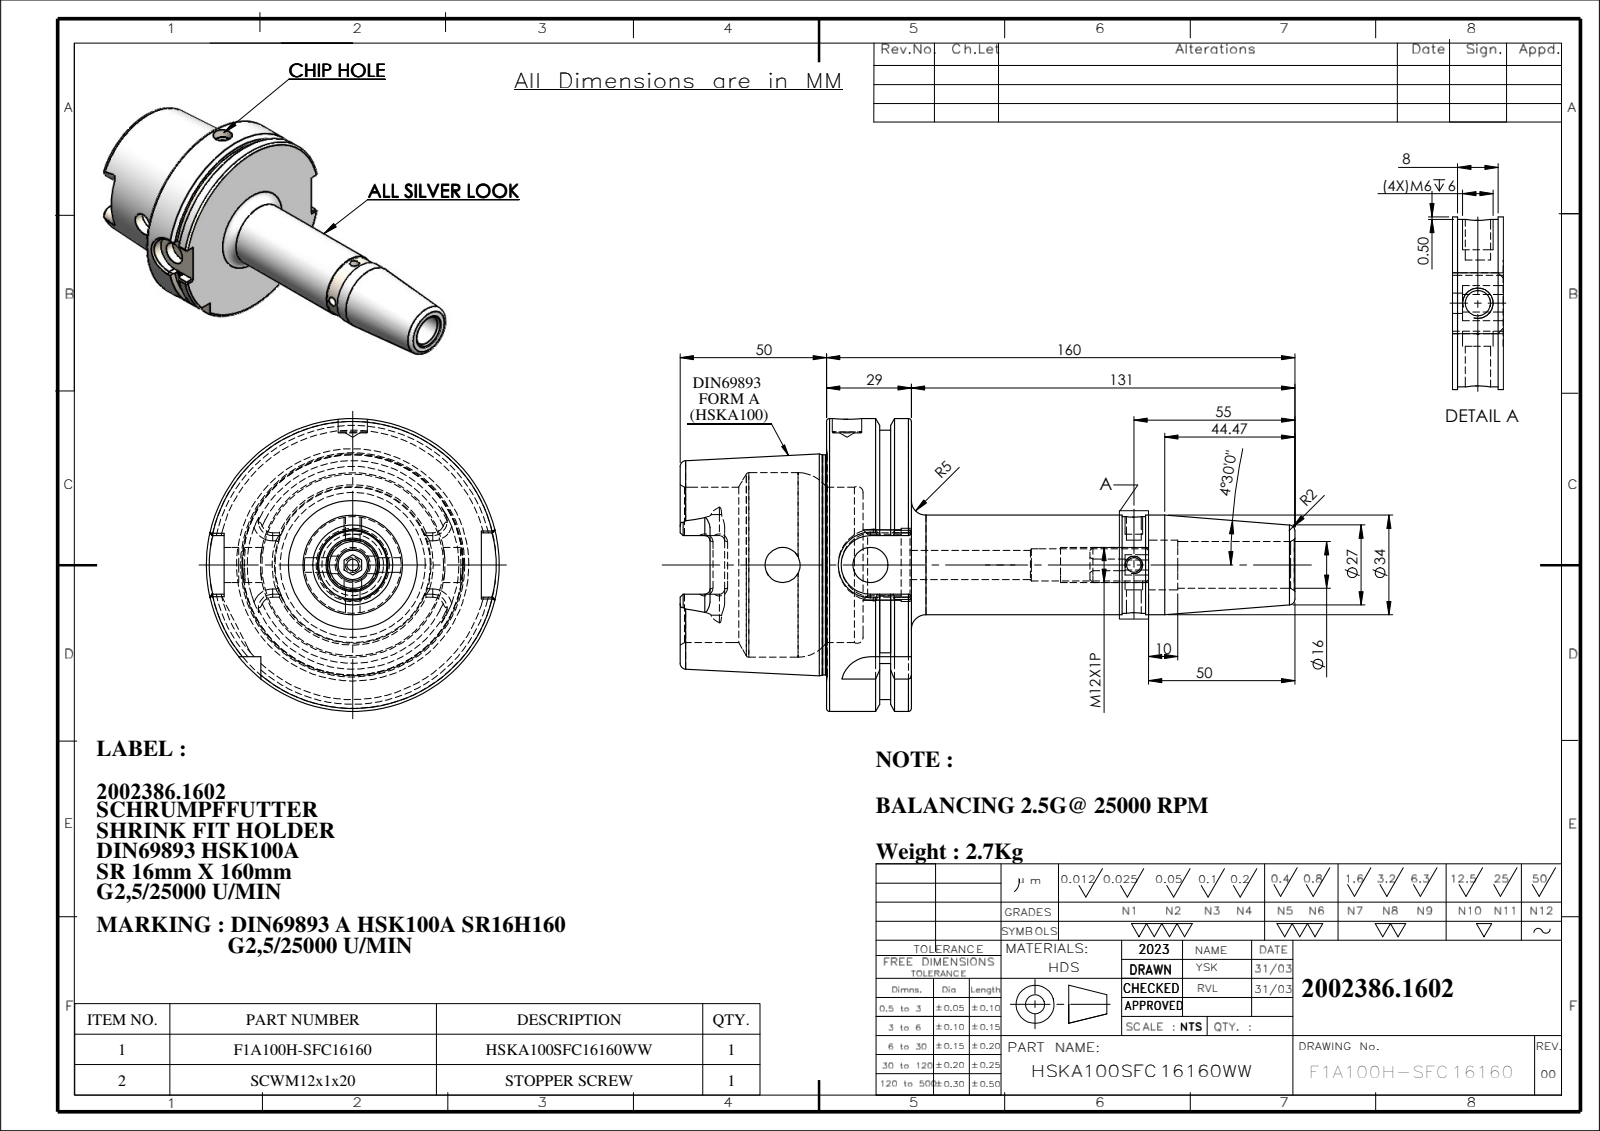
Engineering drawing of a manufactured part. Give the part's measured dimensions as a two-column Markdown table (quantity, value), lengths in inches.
| quantity | value |
| --- | --- |
| part name | HSKA100SFC16160WW; SCWM12X1P; 91100A-SR16160 |
| STEP written by | SolidWorks 2018 (CONFIG_CONTROL_DESIGN) |
| units | inches |
| bodies | 2 solids, 218 faces (68 planar, 70 cylindrical, 80 other) |
| overall size | 8.266 × 3.937 × 3.937 |
| volume | 21.29 in³ |
| surface area | 108 in² |
| round holes (diameter × count) | 0.197 × 2, 0.394 × 2, 0.472 × 2, 0.157 × 1, 0.433 × 1, 0.629 × 1, 0.669 × 1, 0.827 × 1, 0.984 × 1, 2.087 × 1, 2.48 × 1 |
| round bosses / shafts (diameter × count) | 3.937 × 1, 3.622 × 1, 2.959 × 1, 1.339 × 1, 1.299 × 1, 0.472 × 1 |
| partial cylindrical surfaces (radius × count) | 0.071 × 6, 0.192 × 4, 0.394 × 2, 0.433 × 1 |
| main face-to-face distances | 1.14, 0.492, 0.648, 1.969, 2.461, 3.108, 3.091, 1.122, 0.63, 0.018 |
| hole center spacings | 1.181, 3.541, 3.856, 4.722 |
